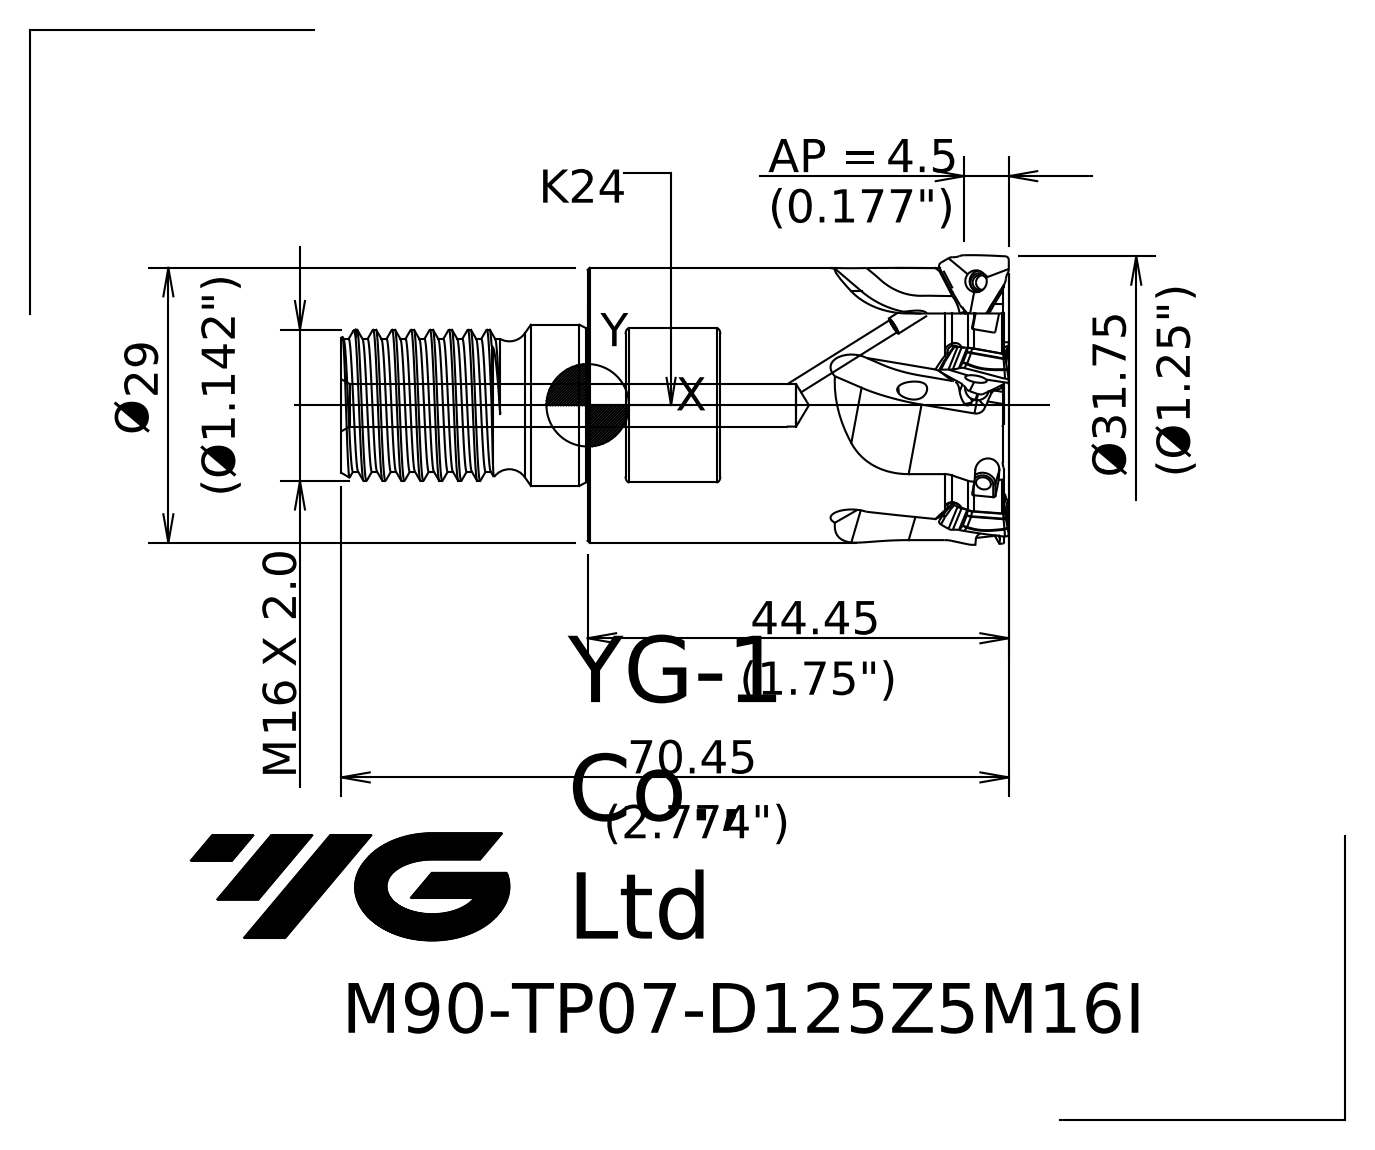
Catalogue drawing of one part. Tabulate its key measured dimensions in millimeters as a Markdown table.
| quantity | value |
| --- | --- |
| part name | 10220A88584A64qr |
| STEP written by | SIEMENS PLM Software NX 10.0 (AP203_CONFIGURATION_CONTROLLED_3D_DESIGN_OF_MECHANICAL_PARTS_AND_ASSEMBLIES_MIM_LF) |
| units | millimeters |
| bodies | 1 solid, 63 faces (11 planar, 10 cylindrical, 42 other) |
| overall size | 70.45 × 31.81 × 31.81 |
| volume | 32 608 mm³ |
| surface area | 9 719 mm² |
| round holes (diameter × count) | 1.5 × 1, 4.5 × 1 |
| round bosses / shafts (diameter × count) | 29 × 1, 17 × 1, 16 × 1, 14 × 1 |
| partial cylindrical surfaces (radius × count) | 0.4 × 4 |
| main face-to-face distances | 43.8, 24, 69.8, 26, 43.95, 69.95, 39.95, 39.8, 4, 30 |
